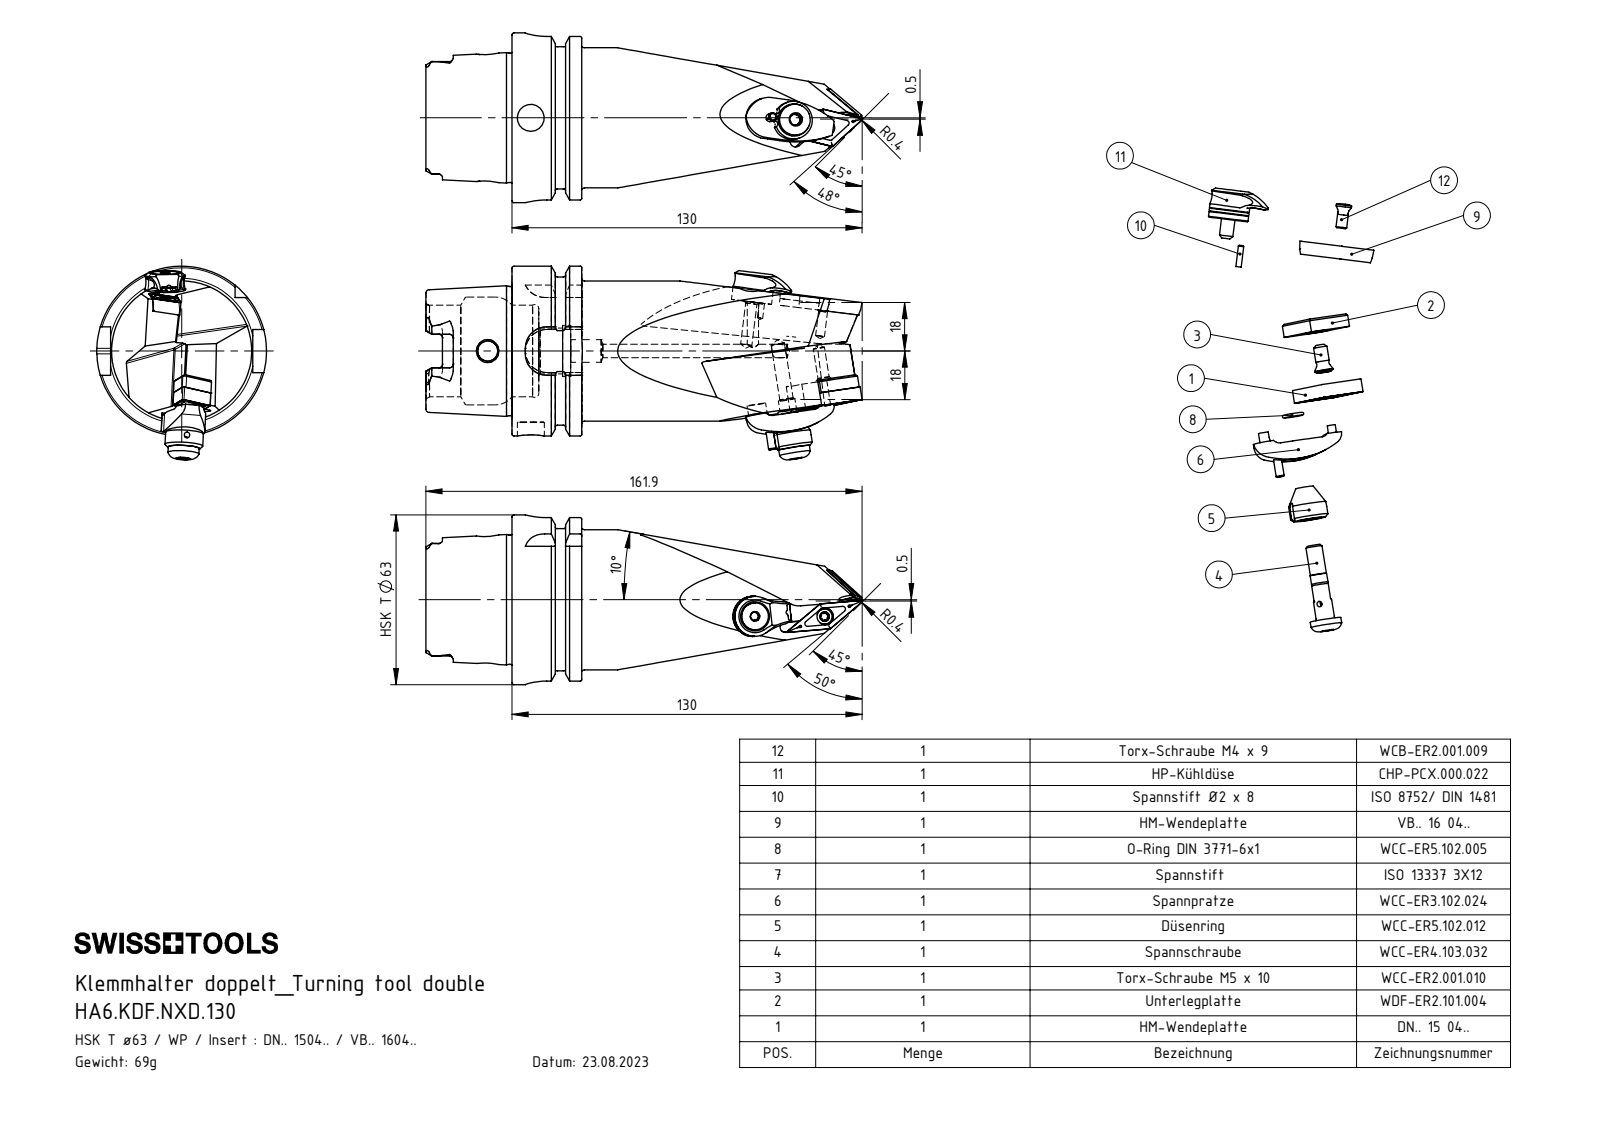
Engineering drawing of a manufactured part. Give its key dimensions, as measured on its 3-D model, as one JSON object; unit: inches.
{"part_name": "WCC-ER5.102.012_B; WCC-ER4.103.032_A; DNMG150404; ISO 13337 - 3 x 12_PreviewCfg (+8 more)", "step_written_by": "SolidWorks 2017 (AUTOMOTIVE_DESIGN)", "units": "inches", "bodies": {"solids": 16, "faces": 750, "planar": 194, "cylindrical": 234, "other": 322}, "overall_size": [6.374, 2.83, 2.48], "volume_in3": 13.9, "surface_area_in2": 72.36, "round_holes": [[0.079, 4], [0.165, 3], [0.197, 2], [0.276, 2], [0.047, 1], [0.094, 1], [0.118, 1], [0.13, 1], [0.173, 1], [0.203, 1], [0.209, 1], [0.24, 1]], "round_bosses_or_shafts": [[0.197, 2], [0.157, 2], [0.118, 2], [2.48, 1], [2.163, 1], [2.047, 1], [1.887, 1], [0.585, 1]], "partial_cylinders_radius": [[0.039, 7], [0.013, 6], [0.015, 6], [0.02, 6], [0.023, 6], [0.027, 6], [0.055, 6], [0.016, 4]], "face_to_face_distances": [1.022, 0.63, 0.392, 1.256, 1.648, 2.278, 0.187, 0.853, 2.079, 0.858], "hole_center_spacings": [0.177, 0.177, 0.315, 0.59, 0.592, 0.905, 0.906, 0.907]}
